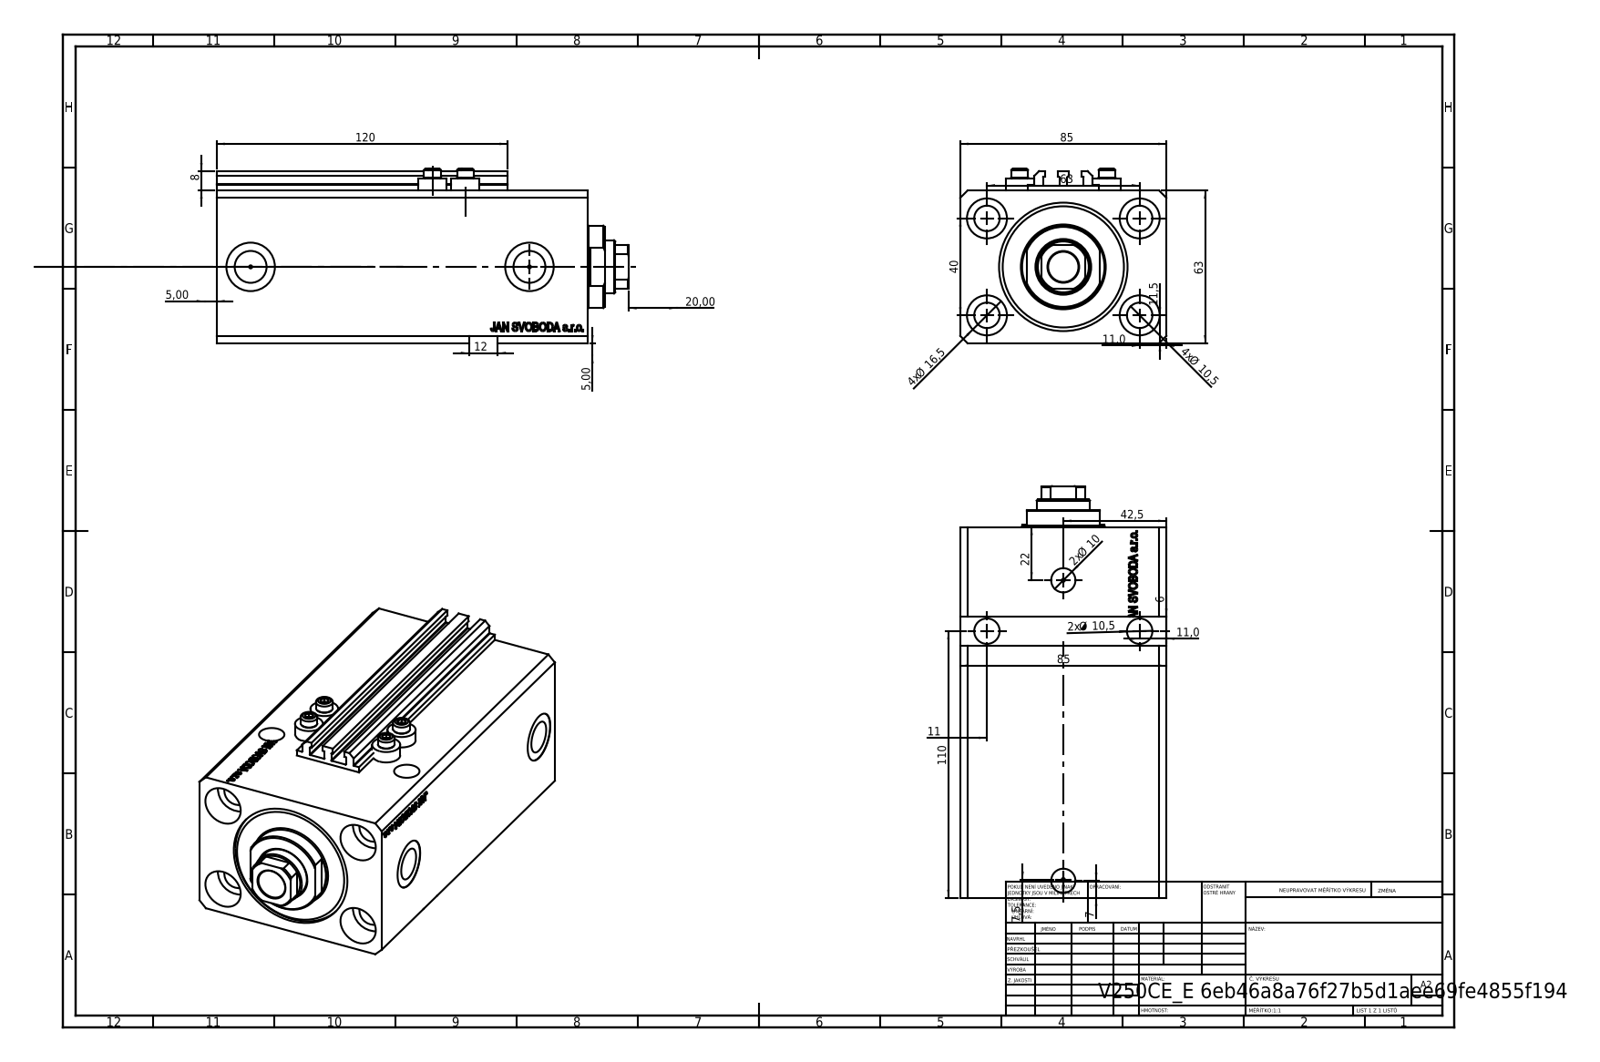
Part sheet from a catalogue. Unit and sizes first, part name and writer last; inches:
Units: inches
Overall size (bounding box): 6.689 × 3.346 × 2.835
Round holes (diameter × count): ⌀0.413 ×6, ⌀0.049 ×4, ⌀0.157 ×4, ⌀0.65 ×4, ⌀0.394 ×2, ⌀0.518 ×2, ⌀0.787 ×2, ⌀0.492 ×1, ⌀0.866 ×1, ⌀1.575 ×1, ⌀2.087 ×1
Round bosses / shafts (diameter × count): ⌀0.457 ×4, ⌀0.276 ×4, ⌀1.339 ×1
Partial cylindrical surfaces — rounded edges, fillets, slot ends (radius × count): R0.008 ×10, R0.413 ×1
Main face-to-face distances: 2.48, 3.346, 6.024, 4.957, 1.067, 0.449, 4.508, 5.575, 2.559, 0.118
Hole centre spacings: 1.469, 2.48, 0.535, 0.606, 0.983, 1.324, 1.417, 1.491
Volume: 41.99 in³ · Surface area: 220.2 in²
Bodies: 8 solids, 1103 faces (539 planar, 138 cylindrical, 426 other)
Part name (STEP PRODUCT): ALLEN BOLT V250CE; V250CE_C_VCP; V250CE_E_Body; V250CE_VC_E
STEP written by: SolidWorks 2019 (CONFIG_CONTROL_DESIGN)
